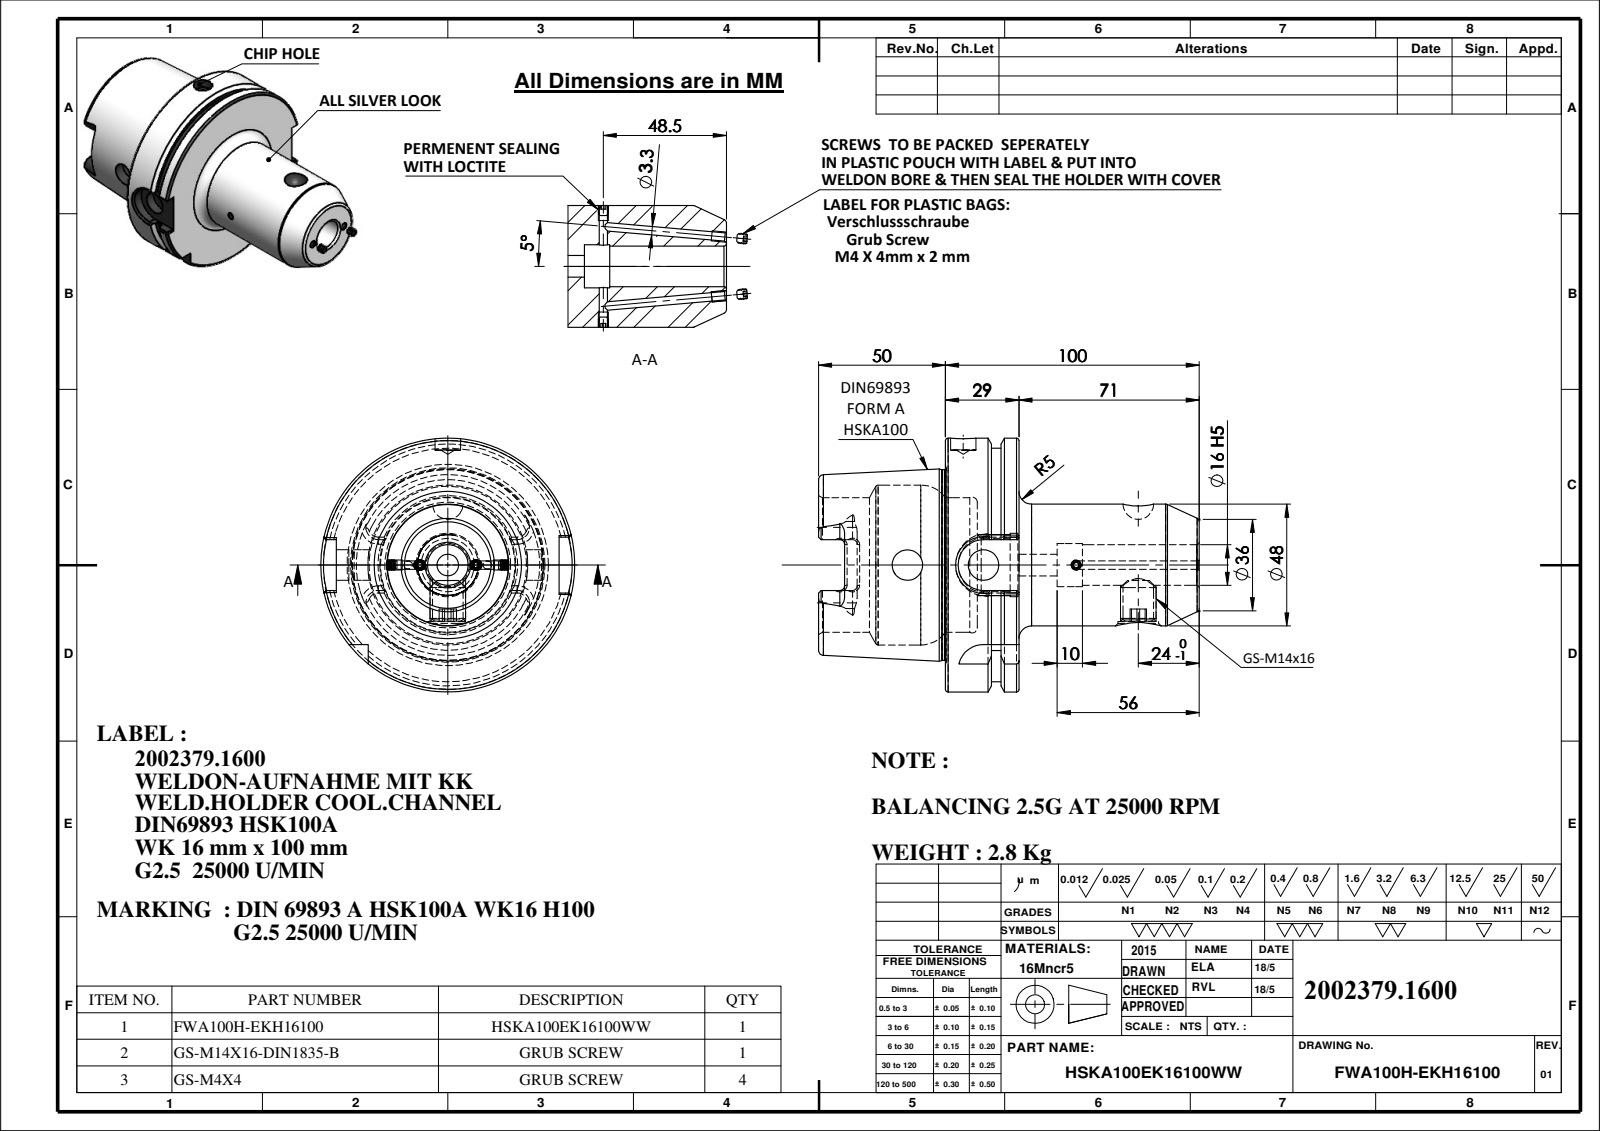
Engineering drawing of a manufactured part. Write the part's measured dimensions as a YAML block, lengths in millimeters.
part_name: "HSKA100EK16100WW-R01; GS-M14X16-DIN1835-B_ISO 4026 - M12 x 12-N; GS-M4X4_DIN 913 - M4 x 4-N; 91100A-WK16100 (+1 more)"
step_written_by: "SolidWorks 2018 (CONFIG_CONTROL_DESIGN)"
units: millimeters
bodies: {solids: 6, faces: 405, planar: 101, cylindrical: 106, other: 198}
overall_size: [158.28, 100, 100]
volume: 364173
surface_area: 65730
round_holes:
  - {diameter: 3.3, count: 3}
  - {diameter: 12, count: 3}
  - {diameter: 16, count: 2}
  - {diameter: 8.5, count: 1}
  - {diameter: 10, count: 1}
  - {diameter: 17, count: 1}
  - {diameter: 21, count: 1}
  - {diameter: 25, count: 1}
  - {diameter: 53, count: 1}
  - {diameter: 63, count: 1}
round_bosses_or_shafts:
  - {diameter: 4, count: 3}
  - {diameter: 100, count: 1}
  - {diameter: 92, count: 1}
  - {diameter: 75.16, count: 1}
  - {diameter: 48, count: 1}
  - {diameter: 14, count: 1}
partial_cylinders:
  - {radius: 1.8, count: 6}
  - {radius: 4.88, count: 4}
  - {radius: 10, count: 2}
  - {radius: 11, count: 1}
face_to_face_distances: [28.95, 16.45, 12.5, 50, 62.5, 78.95, 150, 100, 87.5, 71.05]
hole_center_spacings: [30, 36.5, 66.5, 69]
